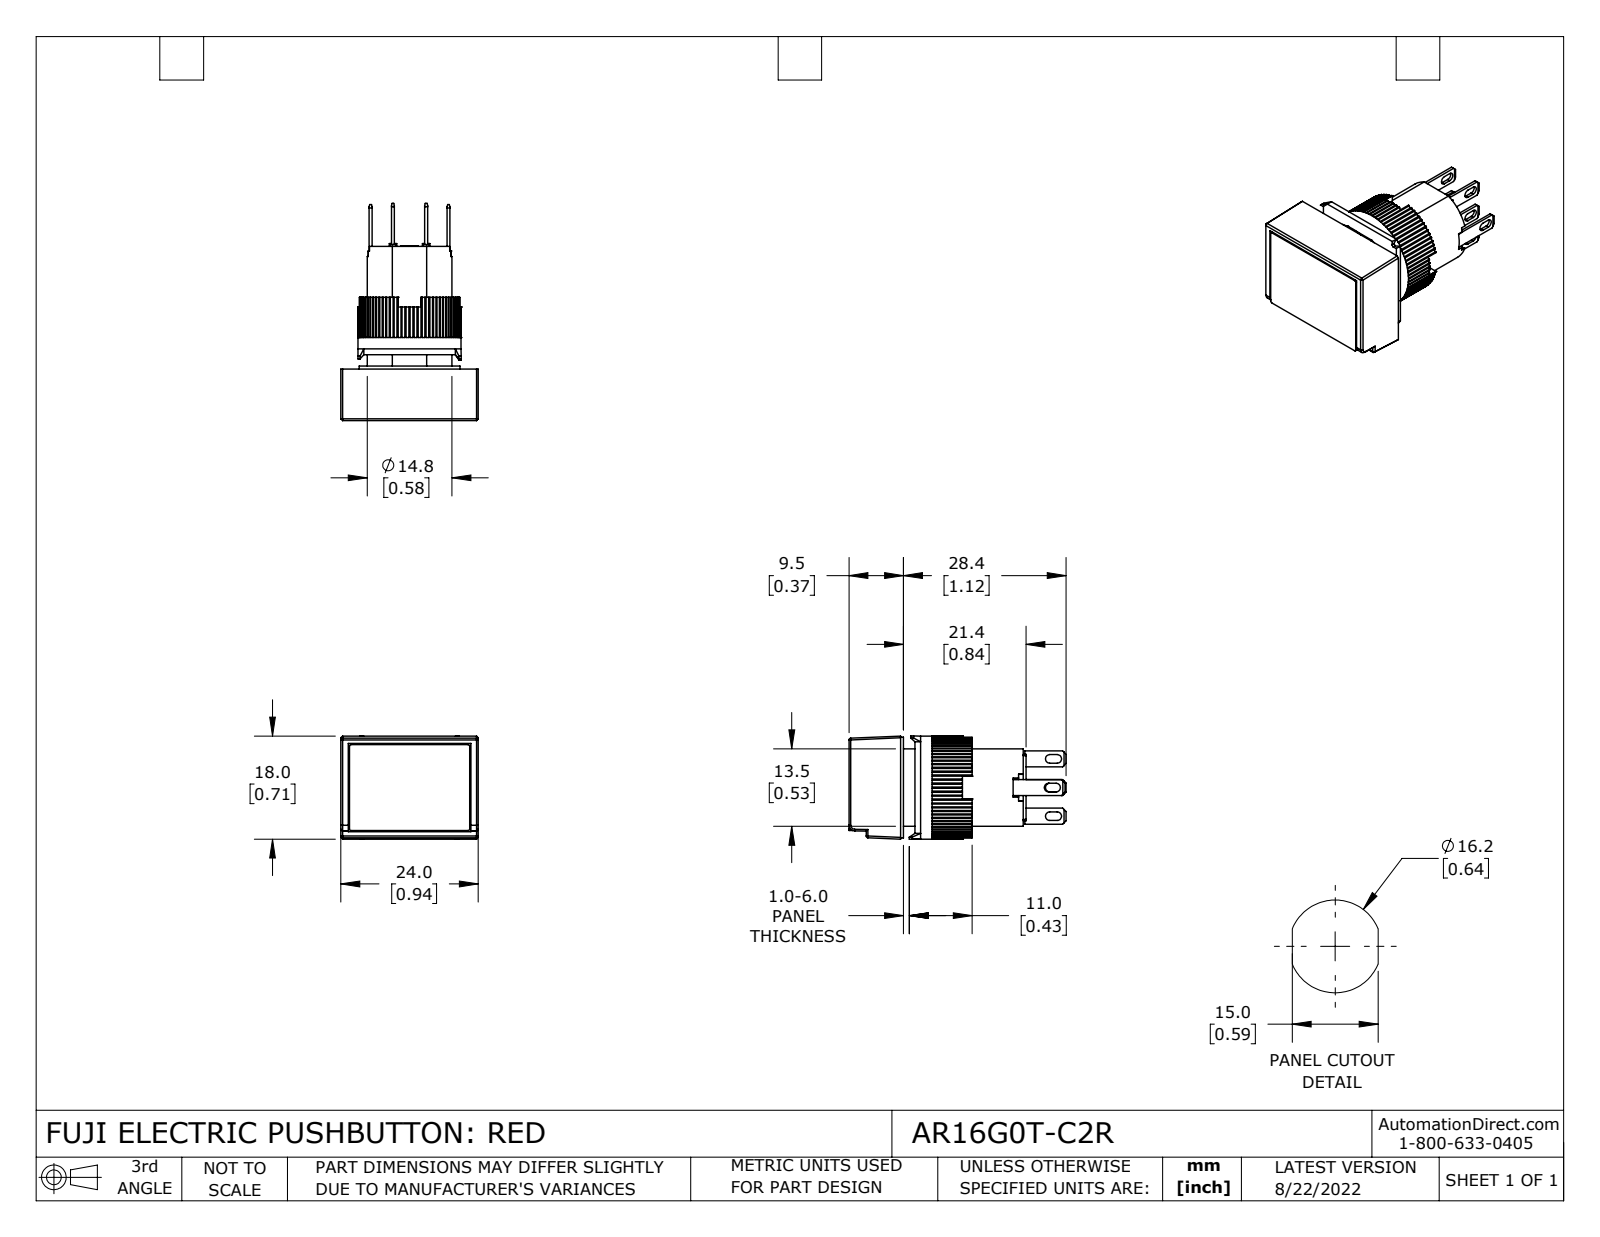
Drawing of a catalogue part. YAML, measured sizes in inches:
part_name: "AR16G0T-C2R"
step_written_by: "SolidWorks 2021 (CONFIG_CONTROL_DESIGN)"
units: inches
bodies: {solids: 14, faces: 841, planar: 654, cylindrical: 181, other: 6}
overall_size: [1.492, 0.945, 0.709]
volume: 0.448
surface_area: 9.503
round_holes:
  - {diameter: 0.543, count: 1}
  - {diameter: 0.583, count: 1}
round_bosses_or_shafts:
  - {diameter: 0.709, count: 1}
  - {diameter: 0.693, count: 1}
partial_cylinders:
  - {radius: 0.01, count: 80}
  - {radius: 0.008, count: 12}
  - {radius: 0.03, count: 8}
  - {radius: 0.012, count: 6}
  - {radius: 0.039, count: 1}
face_to_face_distances: [0.213, 0.354, 0.142, 0.35, 0.492, 0.138, 0.02, 0.843, 0.059, 0.453]
